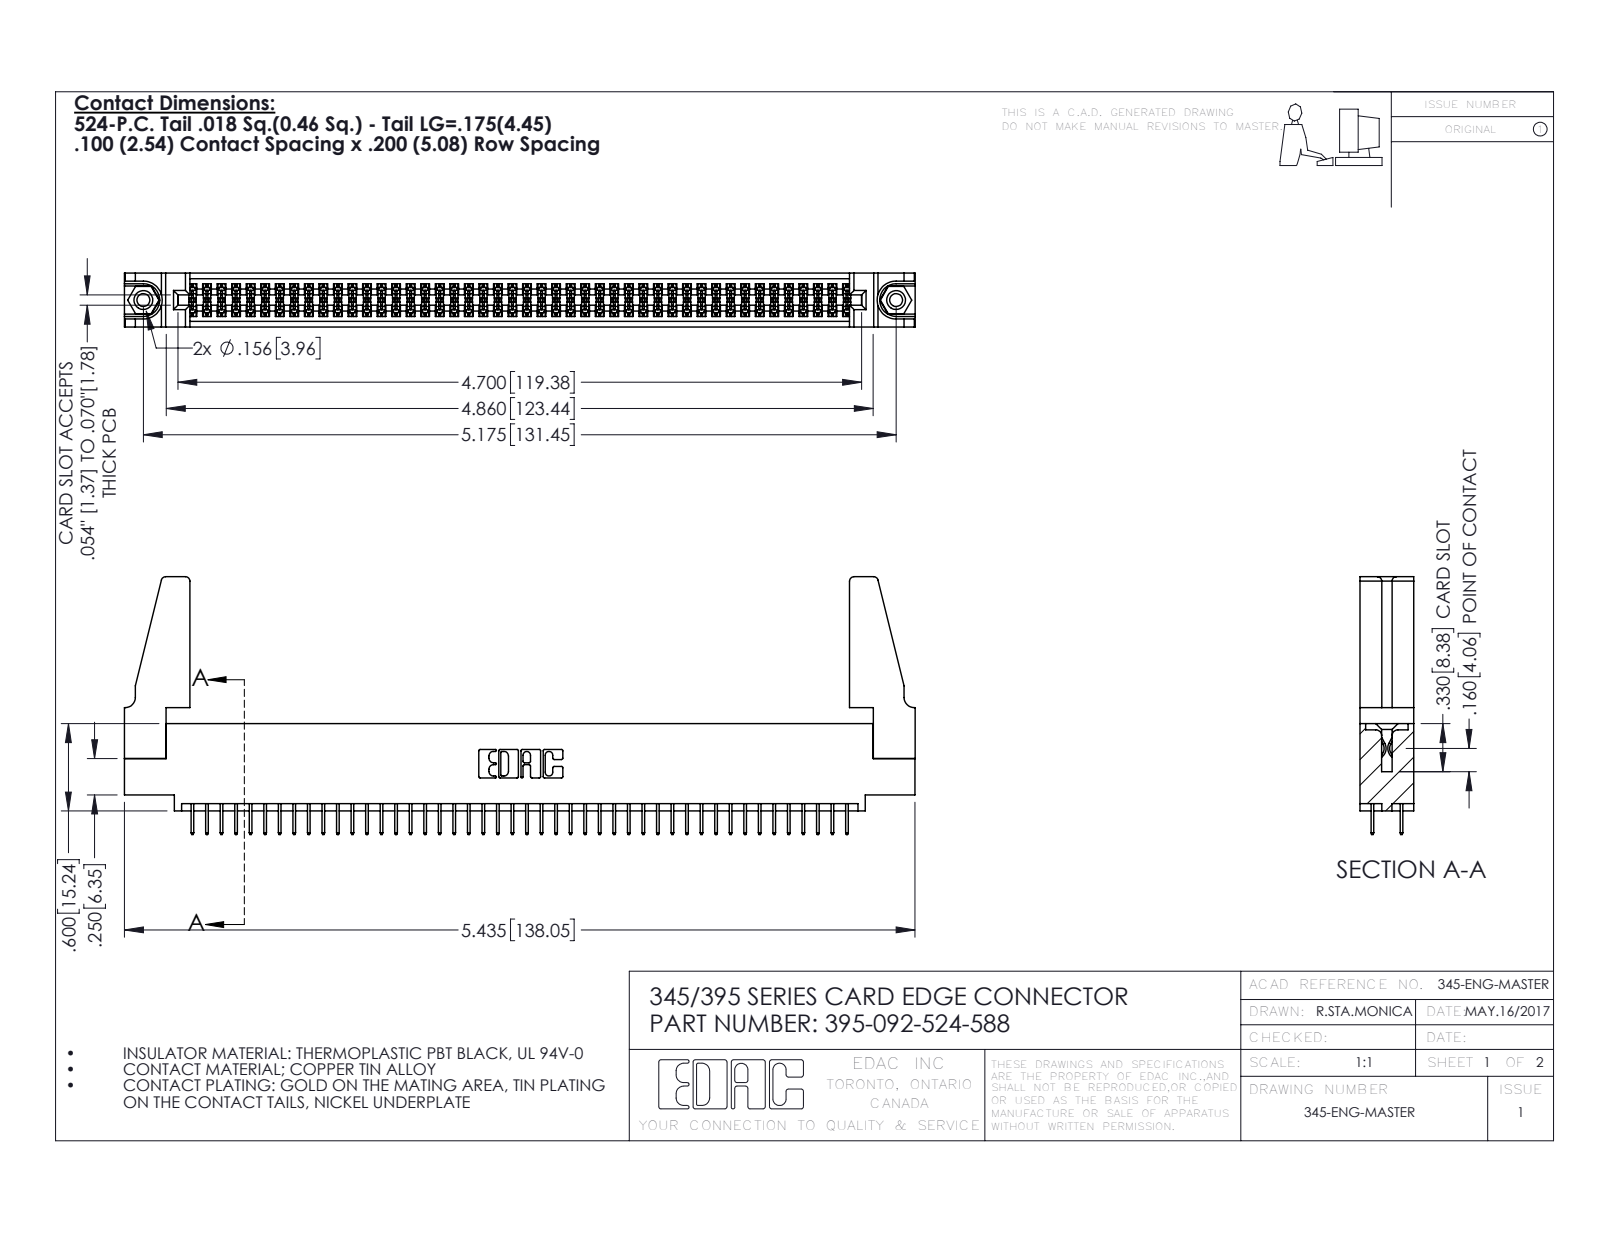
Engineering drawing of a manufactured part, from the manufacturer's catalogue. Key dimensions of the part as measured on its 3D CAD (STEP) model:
Part name (STEP PRODUCT): 395-092-524-588; 345-250-001_345-250-001-102; 345 Part_0.110 Offset - 0.156 Dia-TH; 345-292-001_345-293-124 (+1 more)
STEP written by: SolidWorks 2016 (CONFIG_CONTROL_DESIGN)
Units: inches
Bodies: 97 solids, 5222 faces (3744 planar, 1462 cylindrical, 16 other)
Overall size (bounding box): 5.436 × 1.772 × 0.37
Volume: 1.006 in³ · Surface area: 34.86 in²
Round holes (diameter × count): ⌀0.089 ×2, ⌀0.125 ×2, ⌀0.156 ×2, ⌀0.064 ×1
Round bosses / shafts (diameter × count): ⌀0.155 ×2
Partial cylindrical surfaces — rounded edges, fillets, slot ends (radius × count): R0.006 ×138, R0.01 ×22, R0.03 ×8, R0.007 ×6, R0.031 ×6, R0.026 ×3, R0.014 ×2, R0.019 ×2
Main face-to-face distances: 0.072, 0.298, 0.37, 0.2, 0.098, 0.272, 0.025, 0.225, 0.072, 0.175
Hole centre spacings: 0.27, 4.939, 5.175
